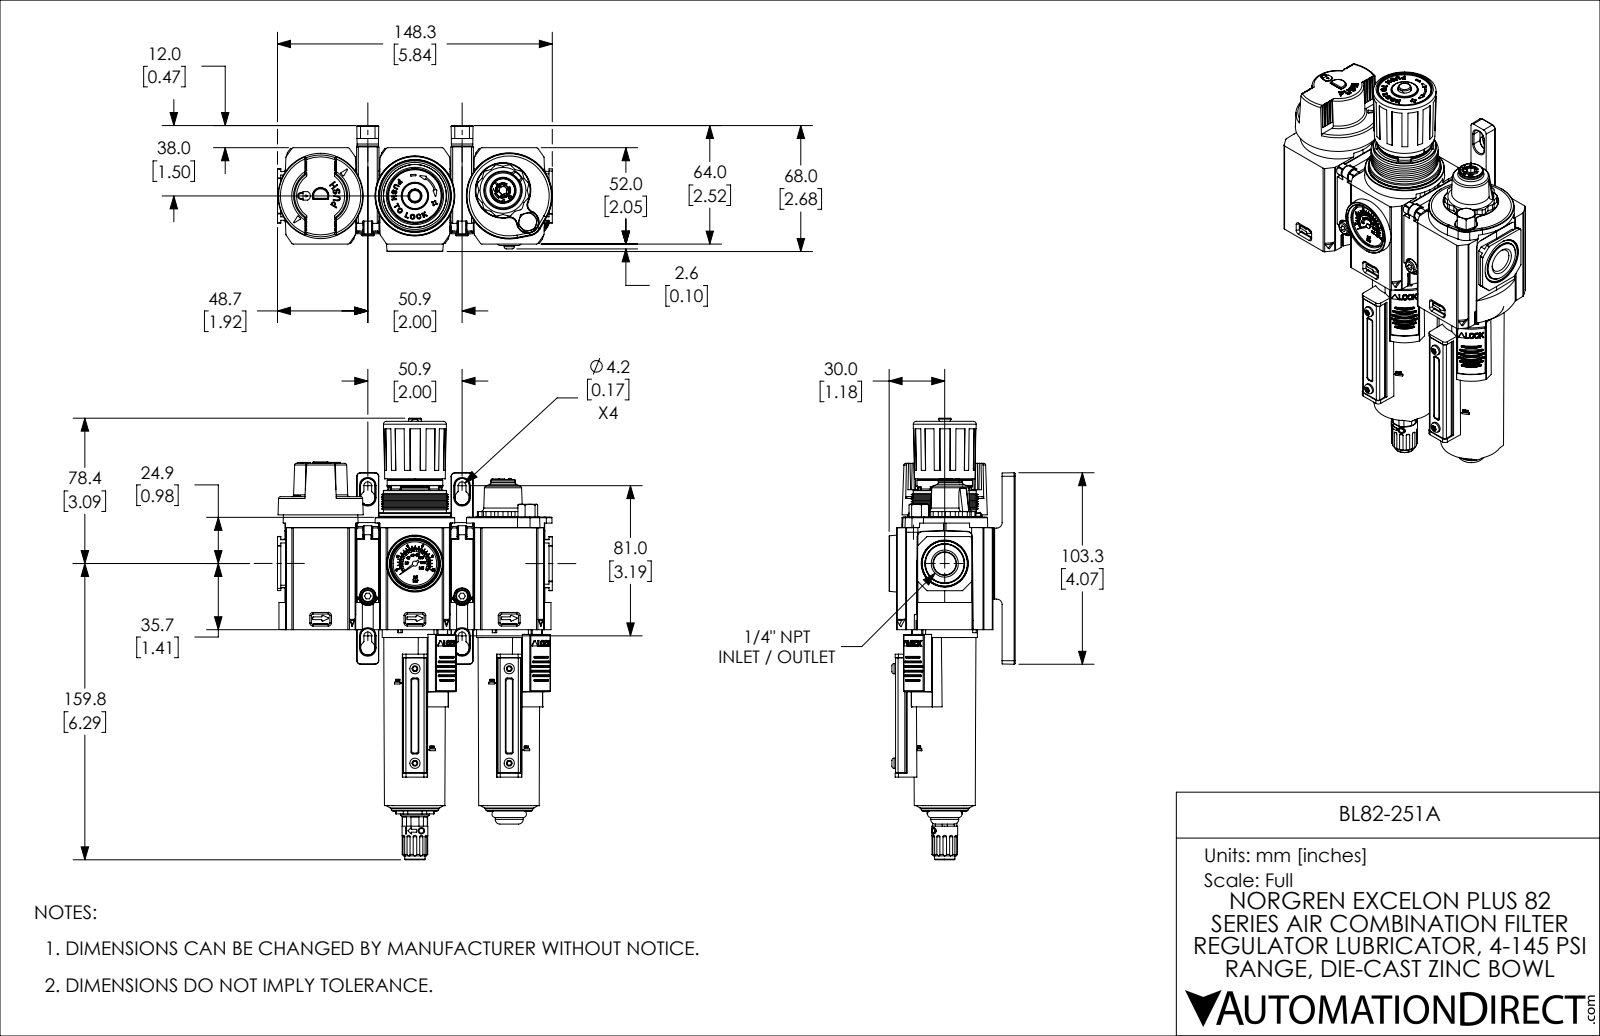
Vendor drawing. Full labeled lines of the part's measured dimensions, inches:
Part name (STEP PRODUCT): BL82-251A
STEP written by: SolidWorks 2021 (CONFIG_CONTROL_DESIGN)
Units: inches
Bodies: 20 solids, 5470 faces (2304 planar, 2204 cylindrical, 962 other)
Overall size (bounding box): 9.379 × 5.839 × 2.676
Volume: 37.65 in³ · Surface area: 326.8 in²
Round holes (diameter × count): ⌀0.097 ×4, ⌀0.306 ×4, ⌀0.039 ×2, ⌀0.128 ×2, ⌀0.138 ×2, ⌀0.175 ×2, ⌀0.187 ×2, ⌀0.628 ×2, ⌀0.098 ×1, ⌀0.106 ×1, ⌀0.128 ×1, ⌀0.197 ×1
Round bosses / shafts (diameter × count): ⌀0.276 ×4, ⌀0.217 ×4, ⌀1.388 ×2, ⌀1.356 ×2, ⌀1.291 ×2, ⌀1.257 ×2, ⌀0.24 ×2, ⌀0.224 ×2
Partial cylindrical surfaces — rounded edges, fillets, slot ends (radius × count): R0.039 ×164, R0.02 ×148, R0.01 ×27, R0.006 ×26, R0.009 ×25, R0.011 ×25, R0.012 ×25, R0.03 ×25
Main face-to-face distances: 0.059, 2.004, 1.988, 2.002, 2.047, 1.929, 4.004, 1.352, 0.182, 0.173
Hole centre spacings: 0.63, 2.004, 0.554, 1.58, 0.59, 0.689, 1.002, 1.091
